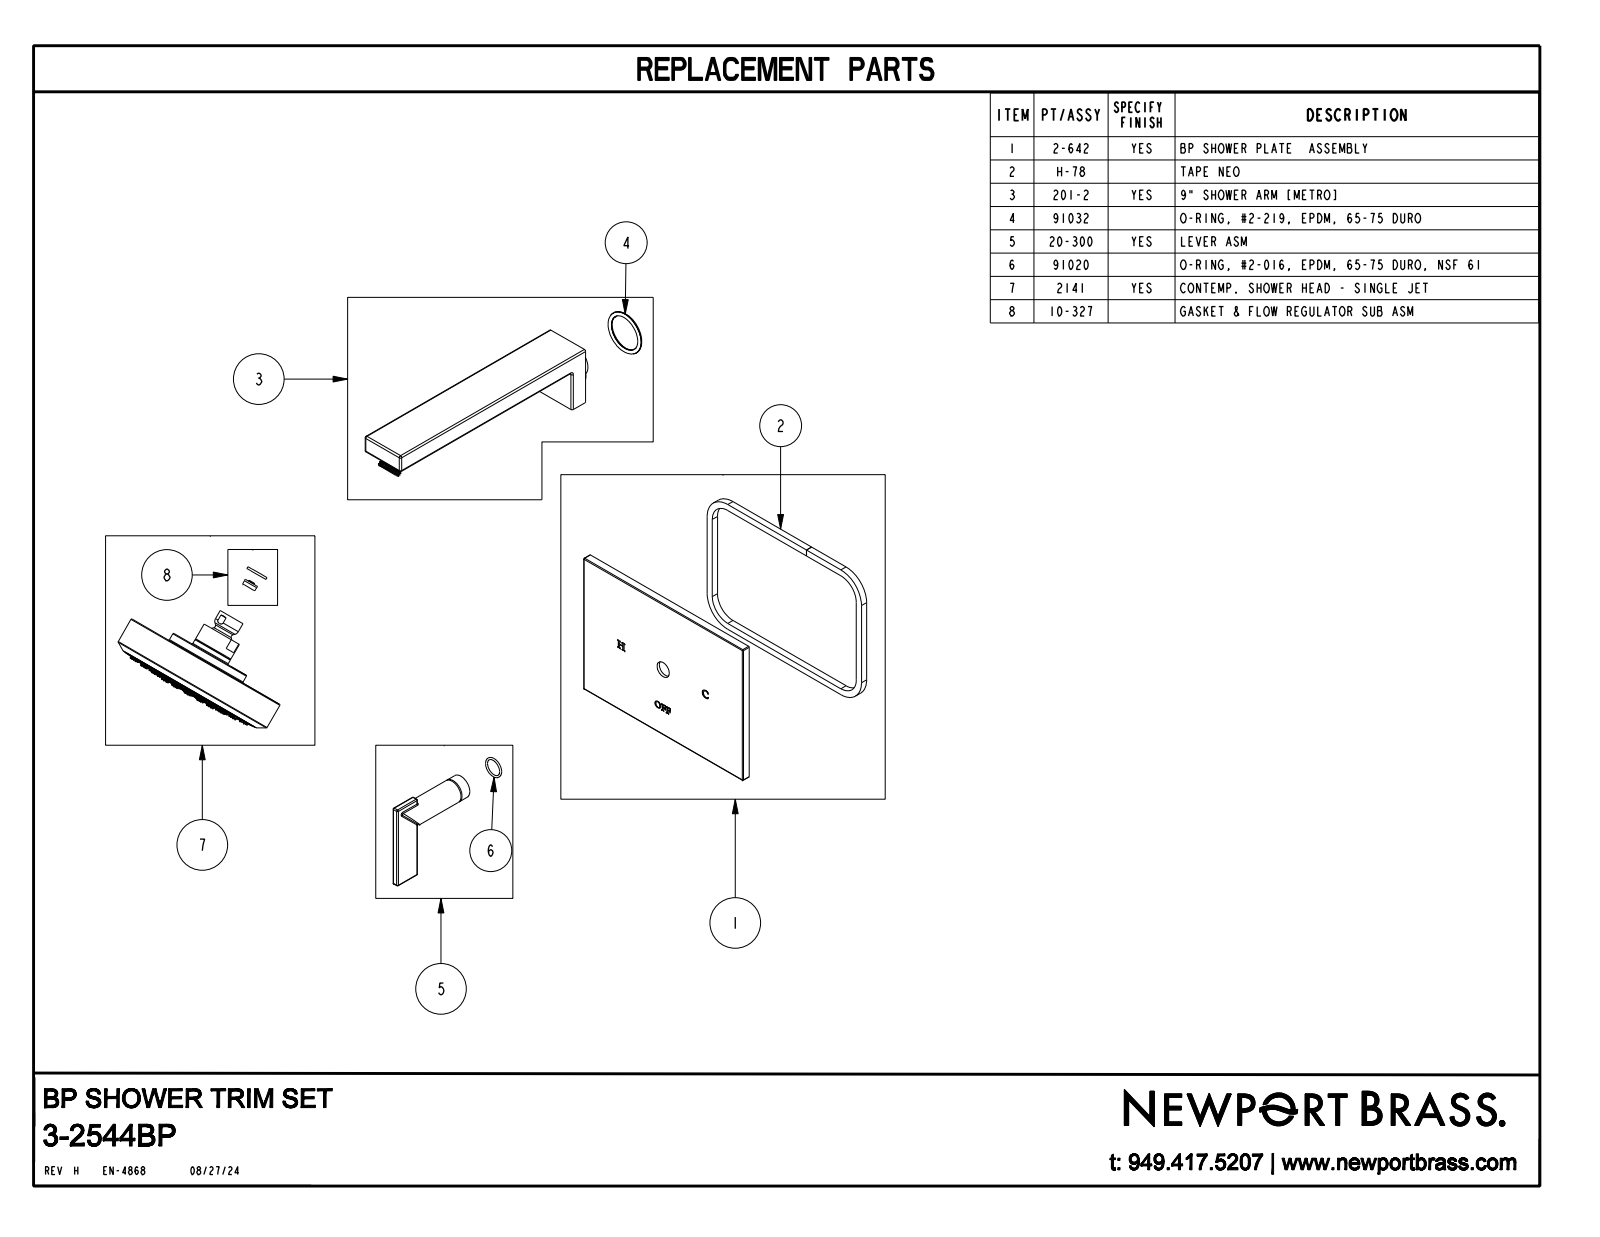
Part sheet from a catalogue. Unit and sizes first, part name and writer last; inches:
Units: inches
Overall size (bounding box): 18.95 × 12.907 × 7.75
Round holes (diameter × count): ⌀0.05 ×90, ⌀0.125 ×90, ⌀0.22 ×1, ⌀0.526 ×1, ⌀0.59 ×1, ⌀0.604 ×1, ⌀0.917 ×1, ⌀1.01 ×1, ⌀1.25 ×1, ⌀4.9 ×1, ⌀5.256 ×1
Round bosses / shafts (diameter × count): ⌀0.198 ×90, ⌀1.4 ×2, ⌀5.91 ×1, ⌀5.22 ×1, ⌀5.1 ×1, ⌀2.92 ×1, ⌀1.75 ×1, ⌀1.1 ×1
Partial cylindrical surfaces — rounded edges, fillets, slot ends (radius × count): R0.125 ×24, R0.04 ×16, R0.06 ×10, R0.03 ×8, R0.532 ×4, R0.08 ×1, R0.452 ×1, R0.475 ×1
Main face-to-face distances: 0.11, 0.06, 0.796, 0.1, 0.896, 0.836, 0.736, 0.654, 0.291, 1.75
Hole centre spacings: 1.84, 1.84, 2.27, 0.48, 0.952, 1.408, 3.187, 3.4
Volume: 32.97 in³ · Surface area: 373.6 in²
Bodies: 64 solids, 1928 faces (397 planar, 836 cylindrical, 695 other)
Part name (STEP PRODUCT): 3-2544BP
STEP written by: CREO PARAMETRIC BY PTC INC, 2018400 (AUTOMOTIVE_DESIGN)
